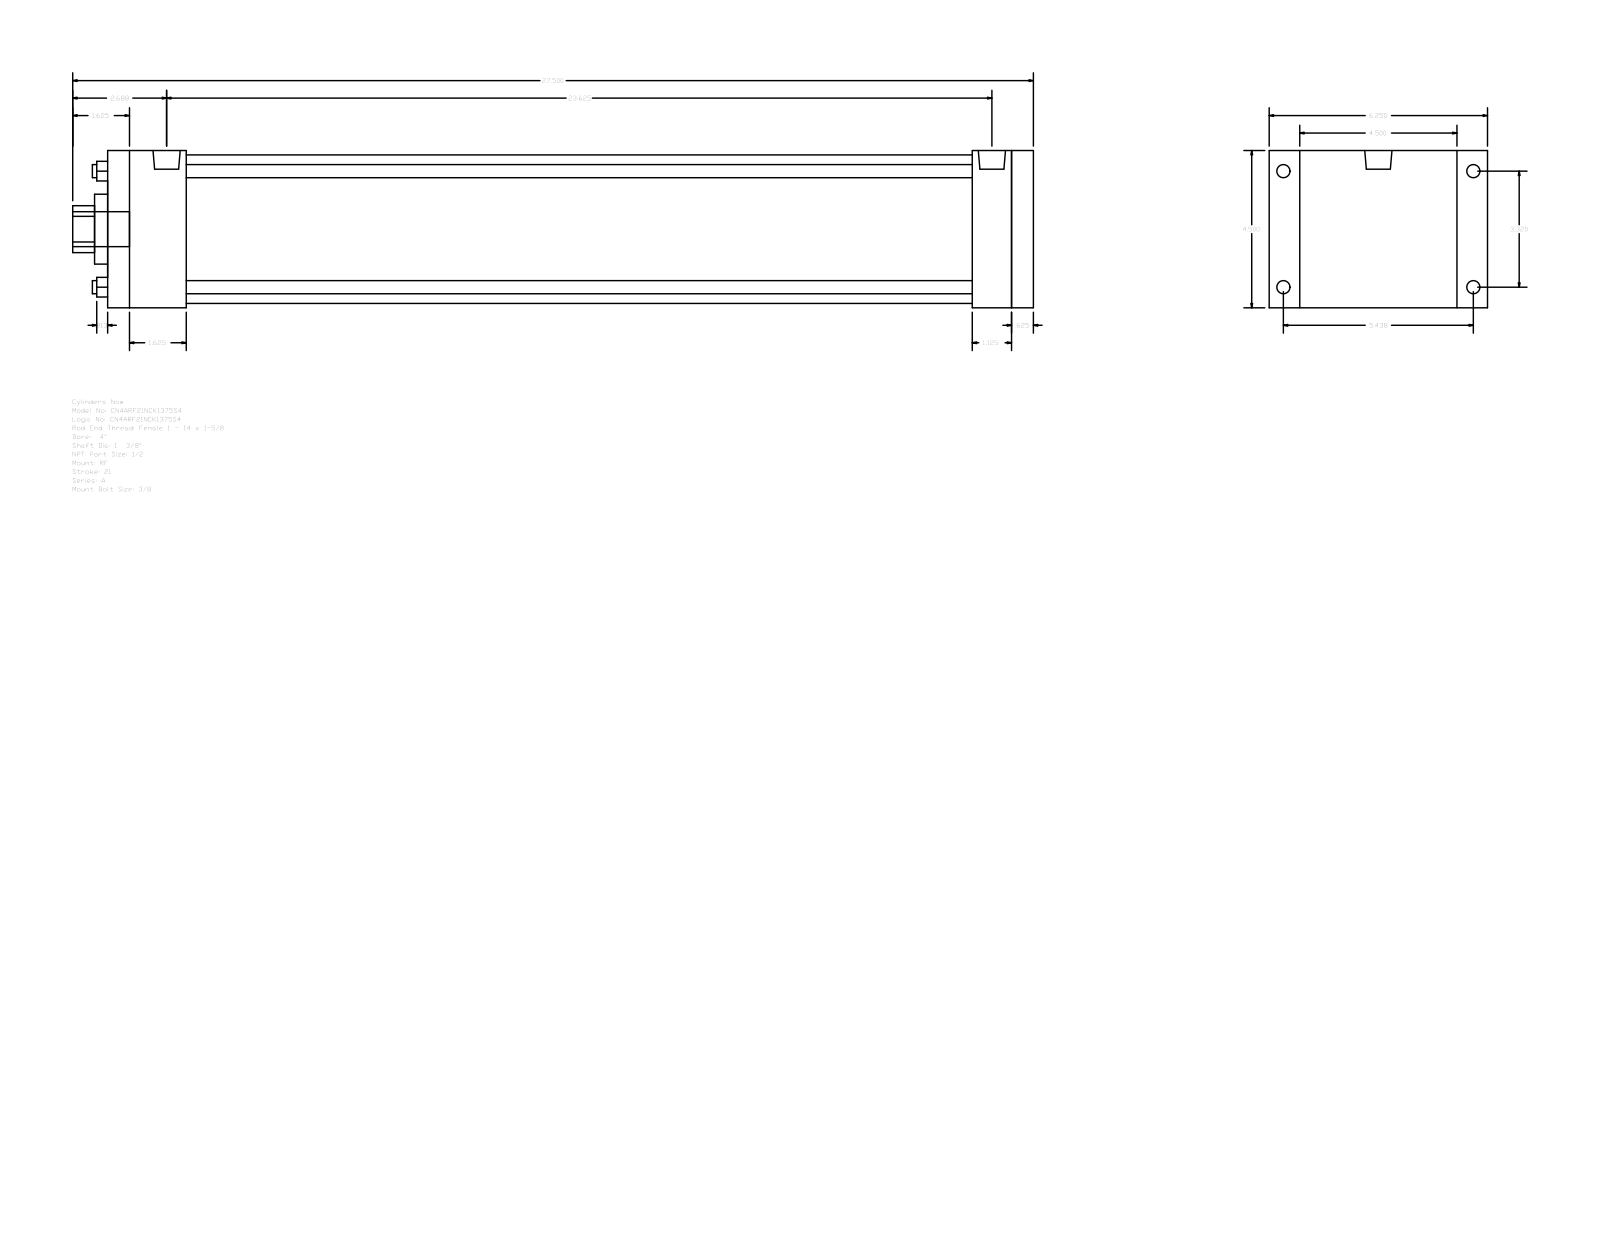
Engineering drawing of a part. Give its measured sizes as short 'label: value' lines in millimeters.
name: A_RF__0400_1.375
written by: GSSL Pune (CONFIG_CONTROL_DESIGN)
unit: mm
bodies: 0 solids, 92 faces (64 planar, 28 cylindrical, 0 other)
size: 698.5 × 158.75 × 114.3
holes: 4× ⌀9.53, 1× ⌀34.92, 1× ⌀50.8, 1× ⌀107.95
bosses: 4× ⌀9.53, 4× ⌀8.73, 2× ⌀19.77, 1× ⌀25.4
rounds: 1× R17.06
face distances: 114.3, 673.1, 15.88, 657.22, 28.57, 22.23, 136.53, 628.65, 44.45, 57.15
hole spacings: 59.62, 84.32, 119.25
